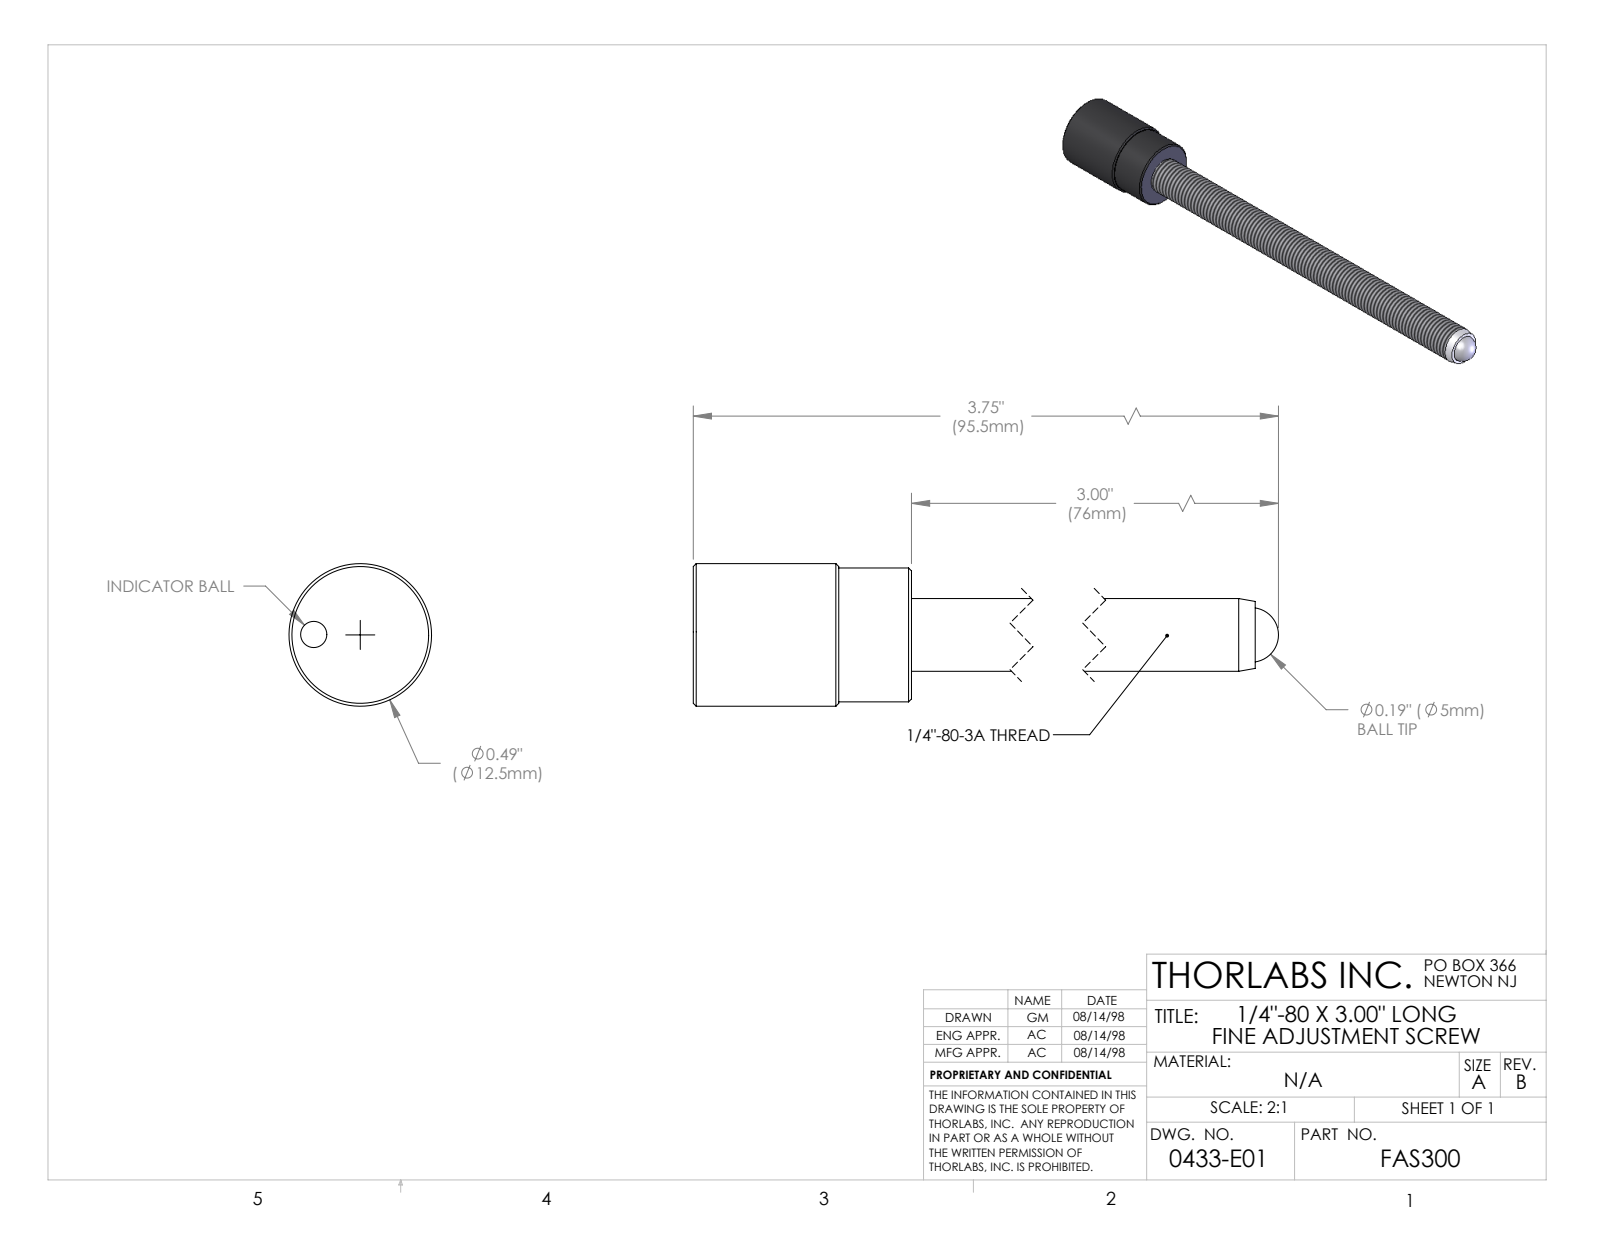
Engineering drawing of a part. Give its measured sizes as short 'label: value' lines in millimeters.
name: 0433-E0W
written by: SolidWorks 2007 (AUTOMOTIVE_DESIGN)
unit: mm
bodies: 4 solids, 40 faces (8 planar, 14 cylindrical, 18 other)
size: 95.25 × 12.45 × 12.45
volume: 4 612 mm³; area: 3 120 mm²
holes: 1× ⌀2.29, 1× ⌀4.78, 1× ⌀5.94, 1× ⌀6.3
bosses: 1× ⌀12.45, 1× ⌀11.68, 1× ⌀6.35
face distances: 19.05, 6.35, 12.7, 93.22, 86.87, 74.17, 80.52, 2.29, 4.06, 10.41
hole spacings: 4.06
